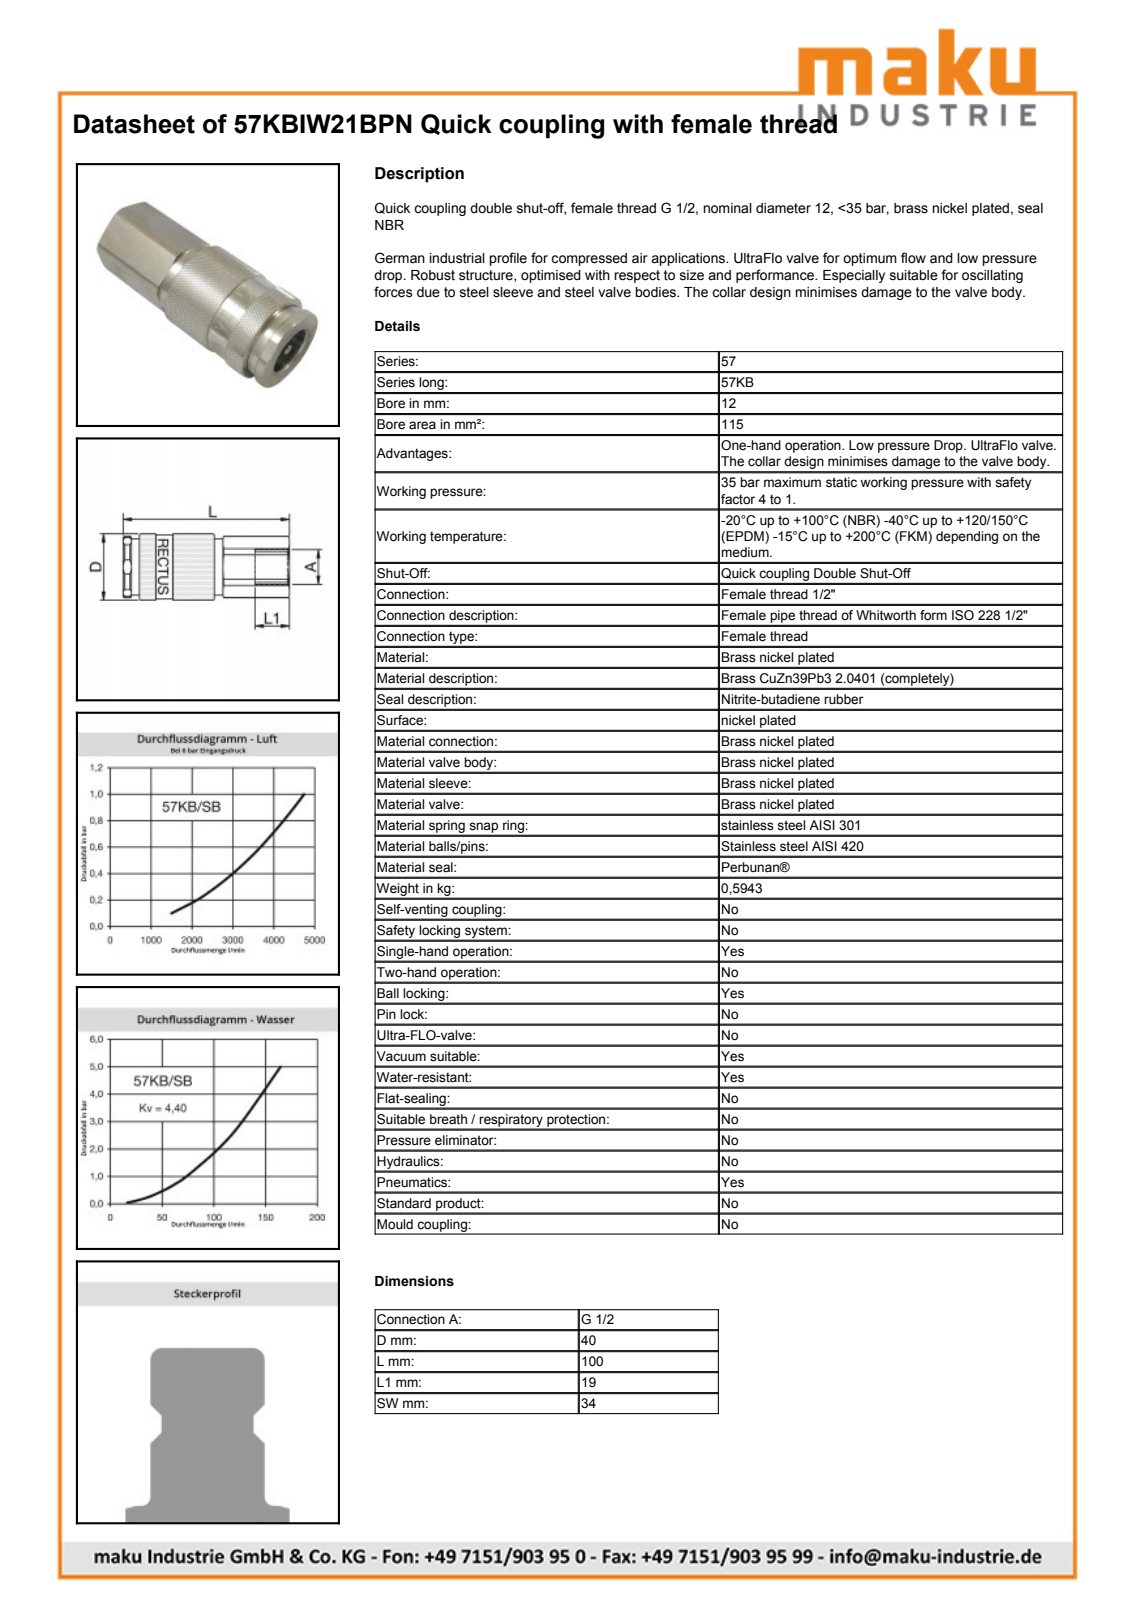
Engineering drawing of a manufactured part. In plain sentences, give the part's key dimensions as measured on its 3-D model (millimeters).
The part is named "D105908". Its 3-D file was written by "Autodesk Inventor 2011 (AUTOMOTIVE_DESIGN)". It is 2 solids with 503 faces: 194 planar, 71 cylindrical and 238 other. Overall it measures 100.05 by 40 by 40 millimeters. Its volume is 99 433 cubic millimeters and its surface area 26 831 square millimeters. Round holes: 1 of diameter 18.63, 1 of diameter 30, 1 of diameter 30.2, 1 of diameter 34.2, 1 of diameter 34.6. Round bosses or shafts: 1 of diameter 40, 1 of diameter 38.5, 1 of diameter 34, 1 of diameter 28.8, 1 of diameter 28.4, 1 of diameter 26.9. Partial cylindrical surfaces (rounded edges, fillets, slot ends): 1 of radius 18.5, 1 of radius 19.15. The main face-to-face distances are 34.02, 33.98, 100.05, 81.01, 19.04, 37.8, 43.21, 62.25, 8.8, 29.
